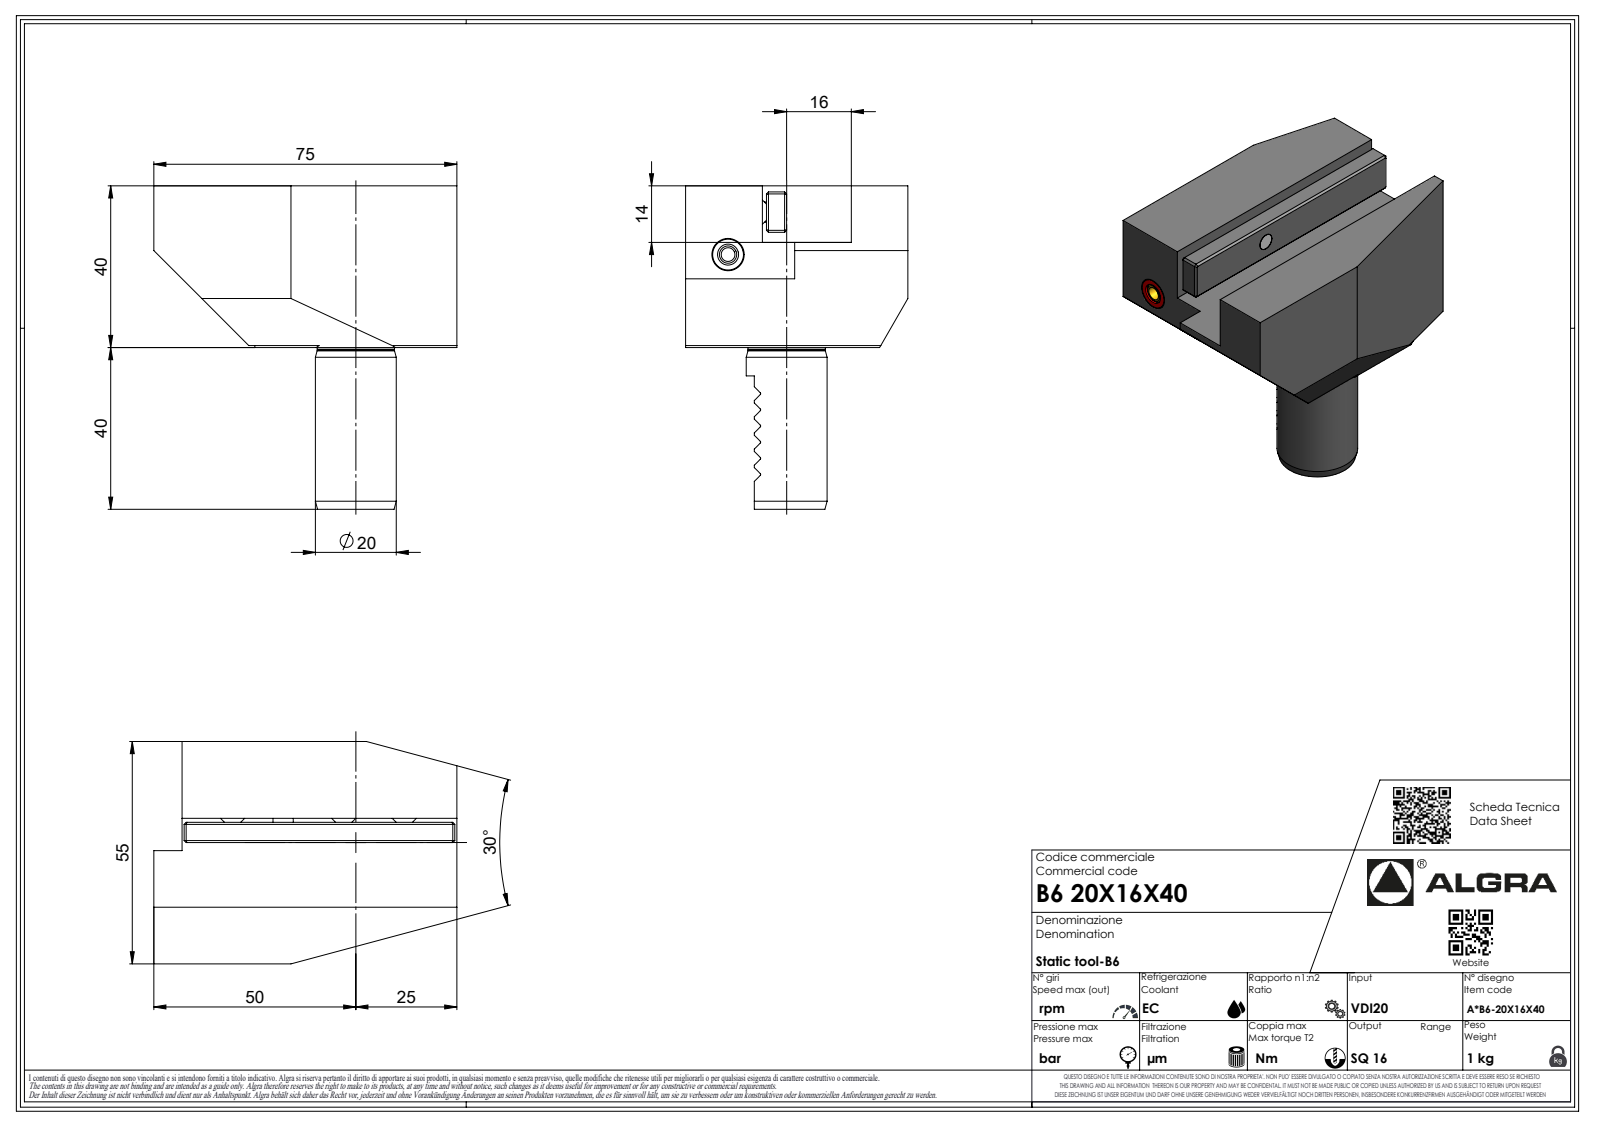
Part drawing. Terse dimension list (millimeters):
name: B620X16X40
written by: SolidWorks 2023 (AUTOMOTIVE_DESIGN)
unit: mm
bodies: 1 solid, 340 faces (243 planar, 36 cylindrical, 61 other)
size: 80 × 75 × 55
volume: 125 831 mm³; area: 20 640 mm²
holes: 1× ⌀2.1
bosses: 1× ⌀50, 1× ⌀20, 1× ⌀19.1, 1× ⌀6.37, 1× ⌀1.7
rounds: 7× R0.33, 7× R0.52, 7× R3.7, 6× R0.3, 1× R0.21
face distances: 14, 40, 26, 41, 55, 0.5, 25, 16, 30, 68
